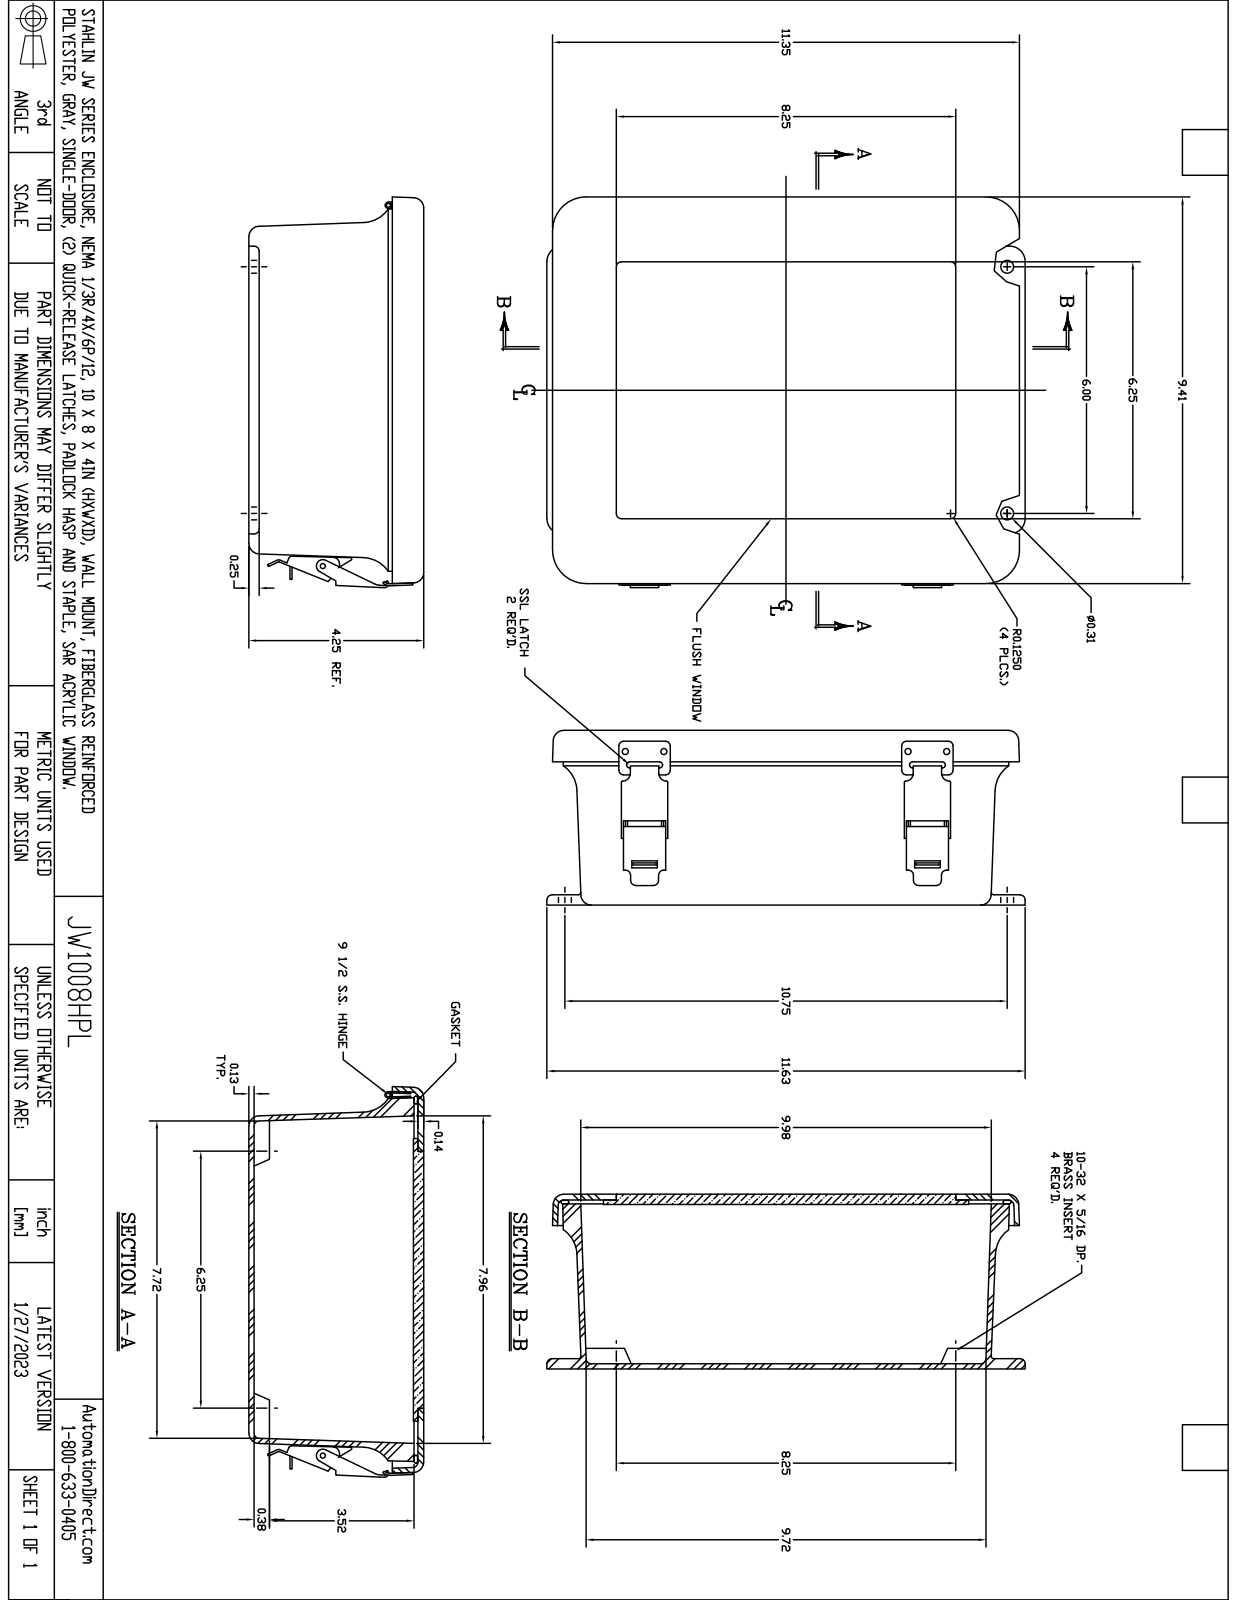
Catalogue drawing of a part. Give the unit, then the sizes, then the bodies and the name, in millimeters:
Units: millimetres
Overall size (bounding box): 295.3 × 242.1 × 107.5
Round holes (diameter × count): ⌀3.6 ×20, ⌀2.6 ×8, ⌀3.3 ×8, ⌀3.9 ×5, ⌀3.3 ×4, ⌀4 ×4, ⌀5.5 ×4, ⌀3.4 ×2, ⌀9.5 ×2, ⌀2.2 ×1, ⌀2.2 ×1
Round bosses / shafts (diameter × count): ⌀3.2 ×13, ⌀6.4 ×8, ⌀6.9 ×4, ⌀3.2 ×3, ⌀7.6 ×1, ⌀4.3 ×1, ⌀3.9 ×1, ⌀3.4 ×1
Partial cylindrical surfaces — rounded edges, fillets, slot ends (radius × count): R3.2 ×24, R0.4 ×20, R0.8 ×20, R1.1 ×16, R0.8 ×12, R6.4 ×12, R0.6 ×8, R1.5 ×6
Main face-to-face distances: 107.5, 6.4, 101.2, 103.9, 3.6, 3.2, 100.8, 104.4, 98, 2.7
Hole centre spacings: 177.8, 178.8, 23.8, 152.4, 19.1, 76.2, 6.4, 19.1
Volume: 1 112 000 mm³ · Surface area: 560 100 mm²
Bodies: 39 solids, 966 faces (414 planar, 405 cylindrical, 147 other)
Part name (STEP PRODUCT): MW1008HPL
STEP written by: SolidWorks 2018 (AUTOMOTIVE_DESIGN)
